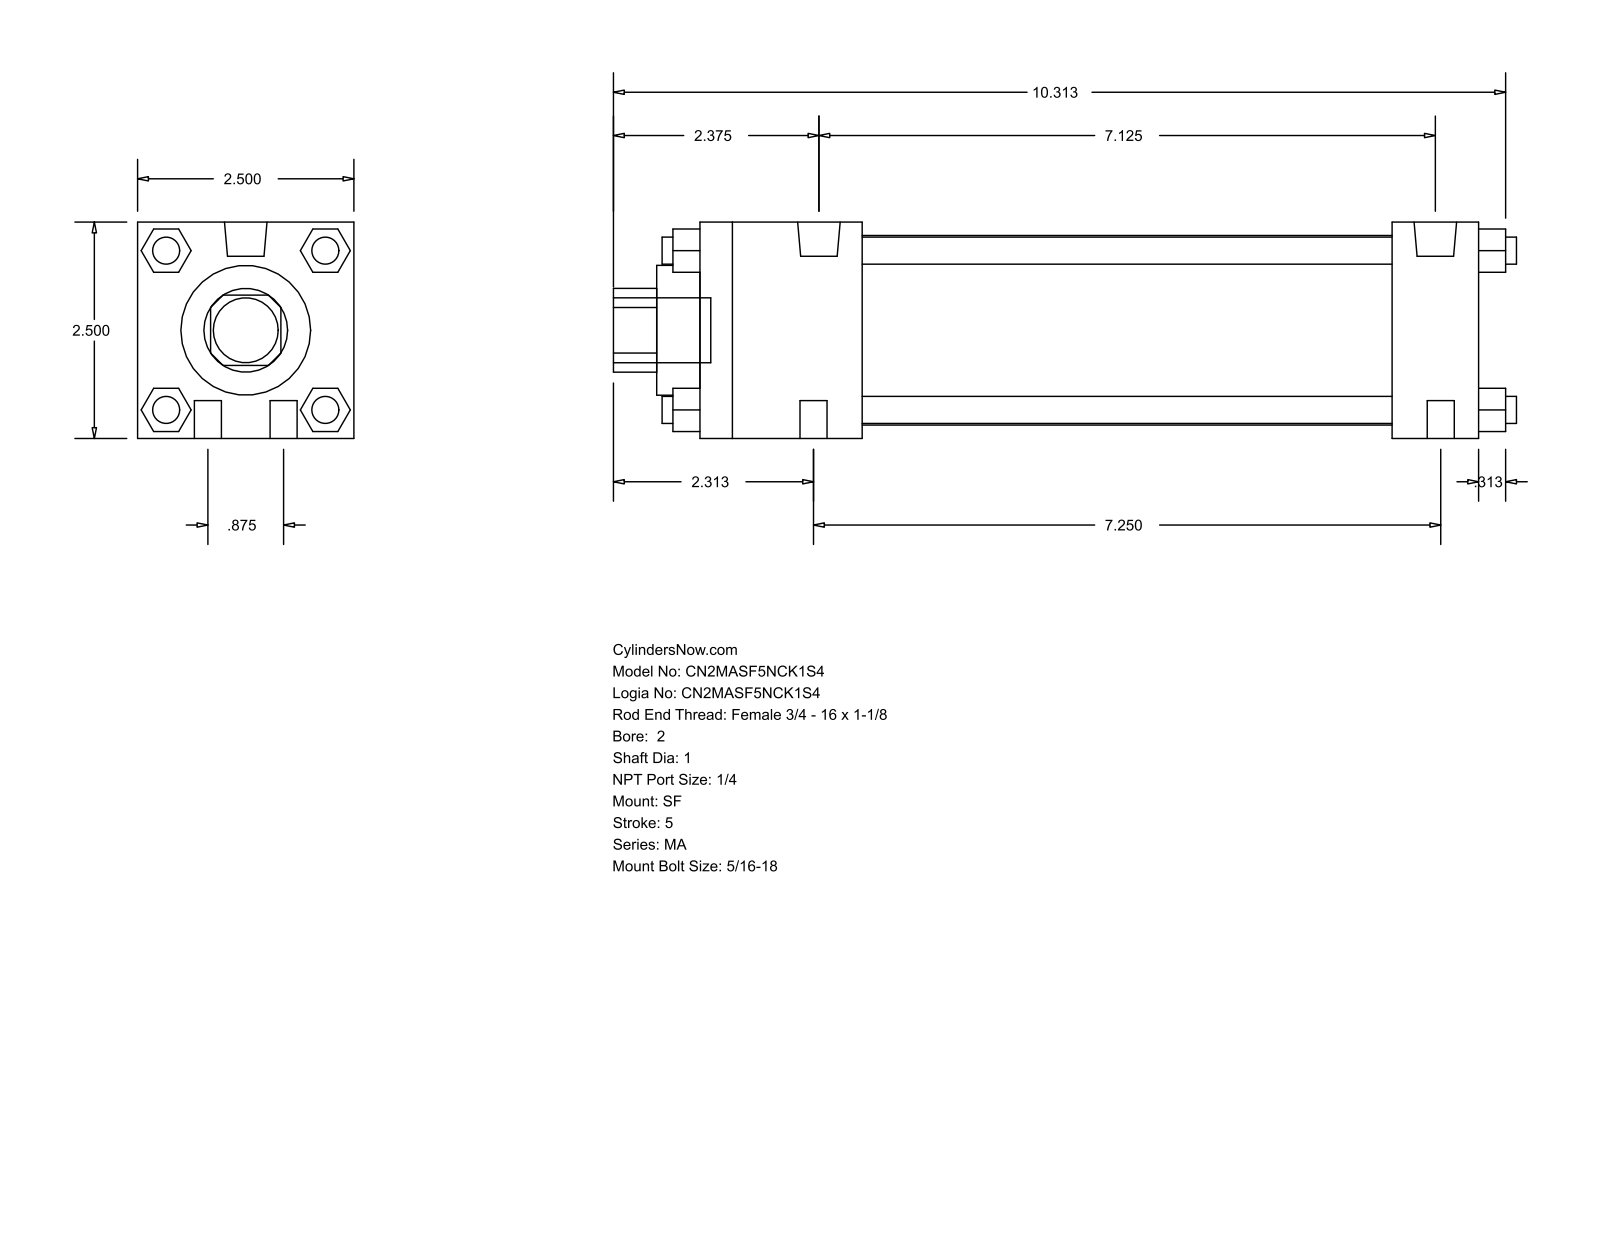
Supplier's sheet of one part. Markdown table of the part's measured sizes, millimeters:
| quantity | value |
| --- | --- |
| part name | MA_SF__0200_1 |
| STEP written by | GSSL Pune (CONFIG_CONTROL_DESIGN) |
| units | millimeters |
| bodies | 0 solids, 124 faces (94 planar, 30 cylindrical, 0 other) |
| overall size | 265.11 × 63.5 × 63.5 |
| round holes (diameter × count) | 25.4 × 1, 38.1 × 1, 55.63 × 1 |
| round bosses / shafts (diameter × count) | 7.94 × 10, 12.49 × 2, 19.05 × 1 |
| partial cylindrical surfaces (radius × count) | 12.29 × 1 |
| main face-to-face distances | 63.5, 228.6, 12.7, 25.4, 203.2, 47.63, 155.57, 180.97, 23.37, 40.47 |
